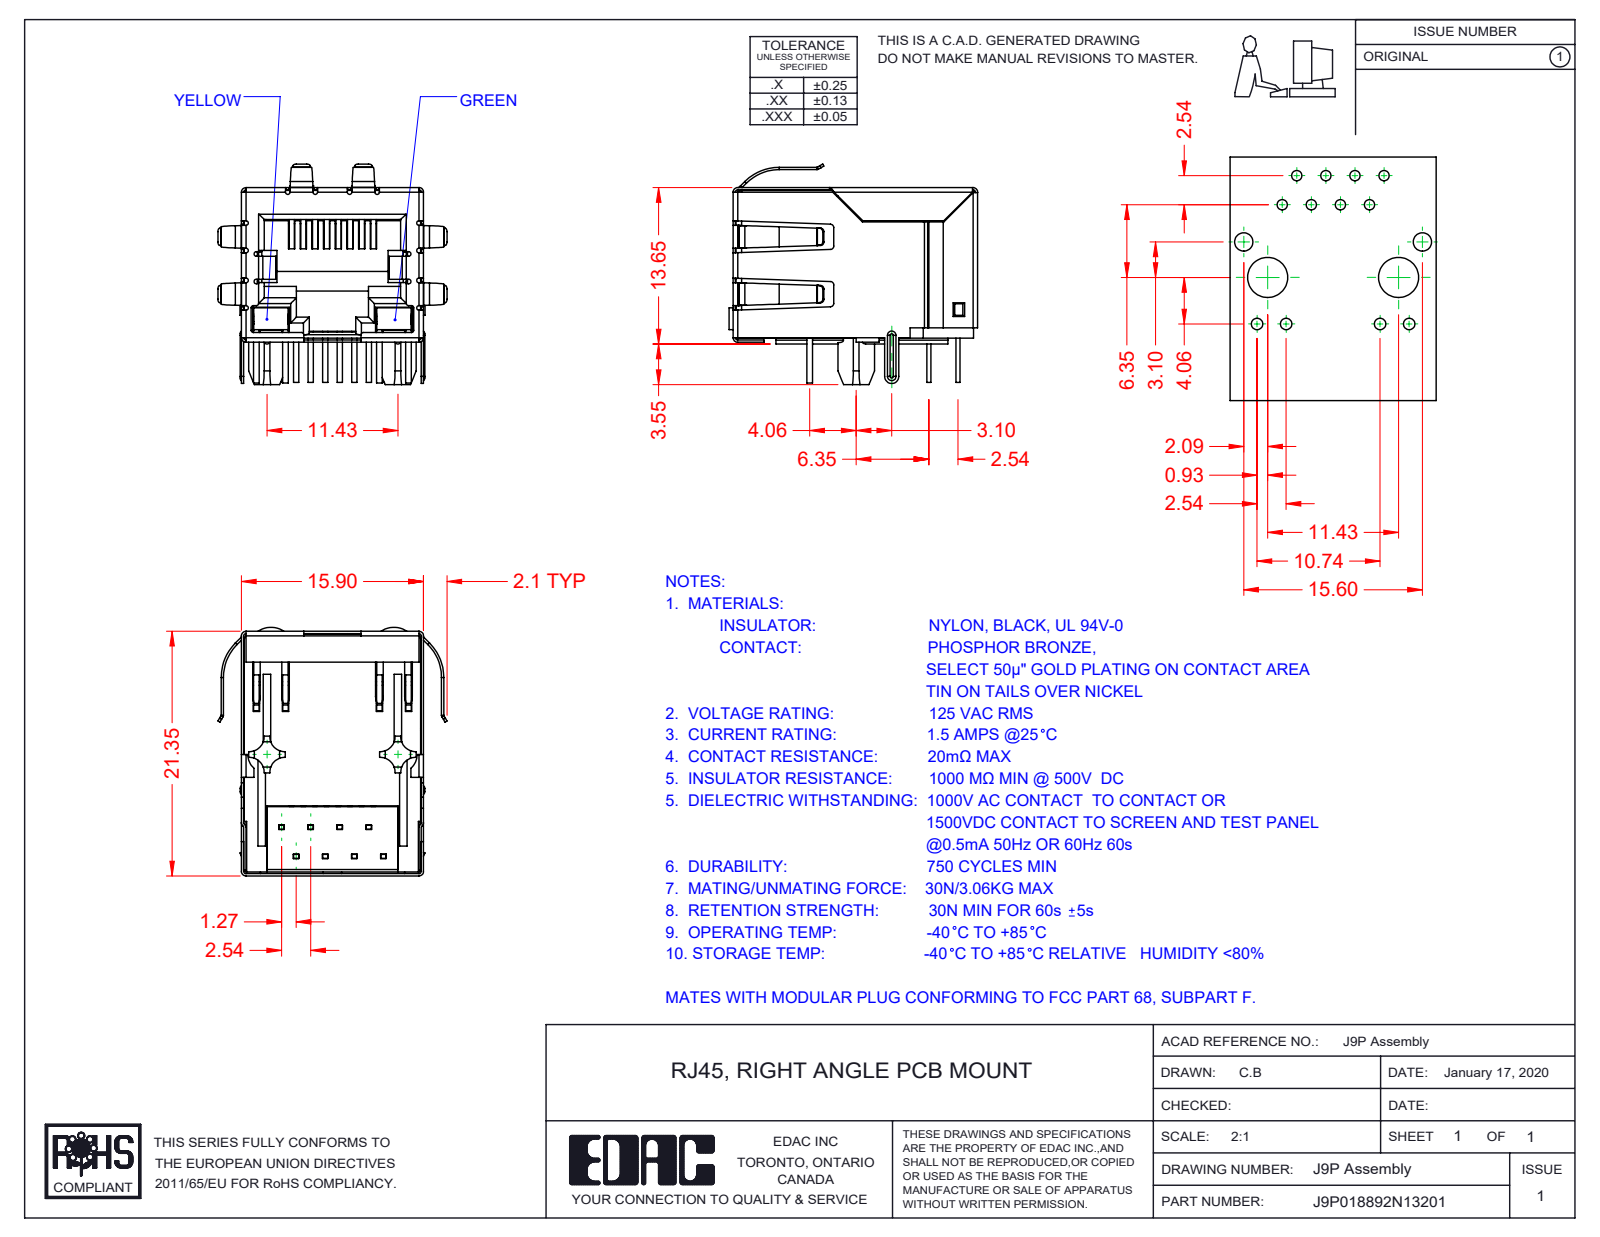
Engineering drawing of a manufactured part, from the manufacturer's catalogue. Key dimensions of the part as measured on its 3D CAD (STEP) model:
Part name (STEP PRODUCT): 9P-LED LED LH_1-Yellow; 9P-LED Contacts; 9P-LED Contact Lock; 9P-LED Insulator (+4 more)
STEP written by: SolidWorks 2016 (CONFIG_CONTROL_DESIGN)
Units: millimetres
Bodies: 13 solids, 1472 faces (1042 planar, 336 cylindrical, 94 other)
Overall size (bounding box): 21.7 × 20 × 19.25
Volume: 2 687 mm³ · Surface area: 7 515 mm²
Partial cylindrical surfaces — rounded edges, fillets, slot ends (radius × count): R0.2 ×39, R0.5 ×22, R0.3 ×20, R0.4 ×16, R1.3 ×8, R0.23 ×5, R0.11 ×4, R0.31 ×4
Main face-to-face distances: 15.45, 15.7, 15.65, 0.35, 0.54, 15.5, 12.36, 0.6, 1.4, 0.59
